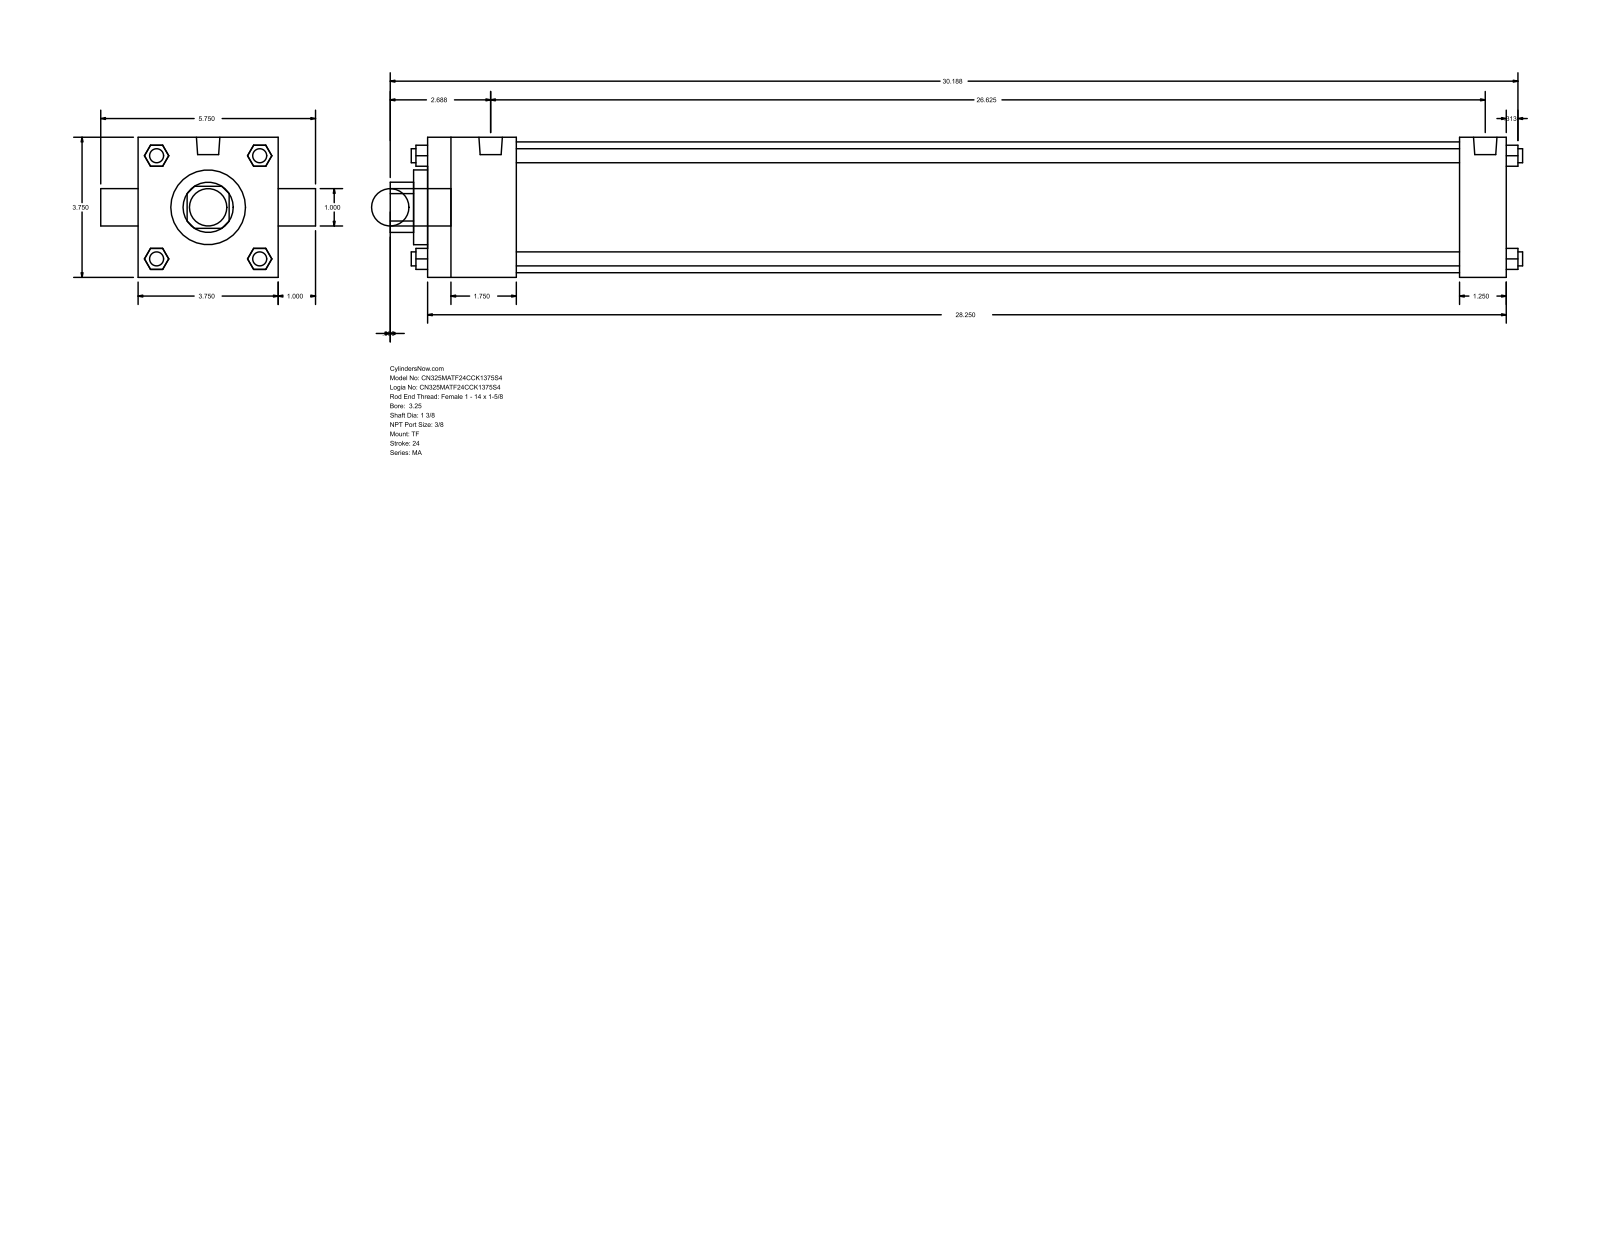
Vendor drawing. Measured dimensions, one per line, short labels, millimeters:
name: MA_TF__0325_1.375
written by: GSSL Pune (CONFIG_CONTROL_DESIGN)
unit: mm
bodies: 0 solids, 120 faces (92 planar, 28 cylindrical, 0 other)
size: 769.94 × 146.05 × 95.25
holes: 1× ⌀25.4, 1× ⌀34.92, 1× ⌀50.8, 1× ⌀88.9
bosses: 4× ⌀9.53, 3× ⌀11.11, 2× ⌀15.93, 1× ⌀25.4
rounds: 1× R17.06
face distances: 95.24, 733.43, 60.32, 701.68, 641.36, 673.11, 31.75, 9.52, 69.84, 711.2
